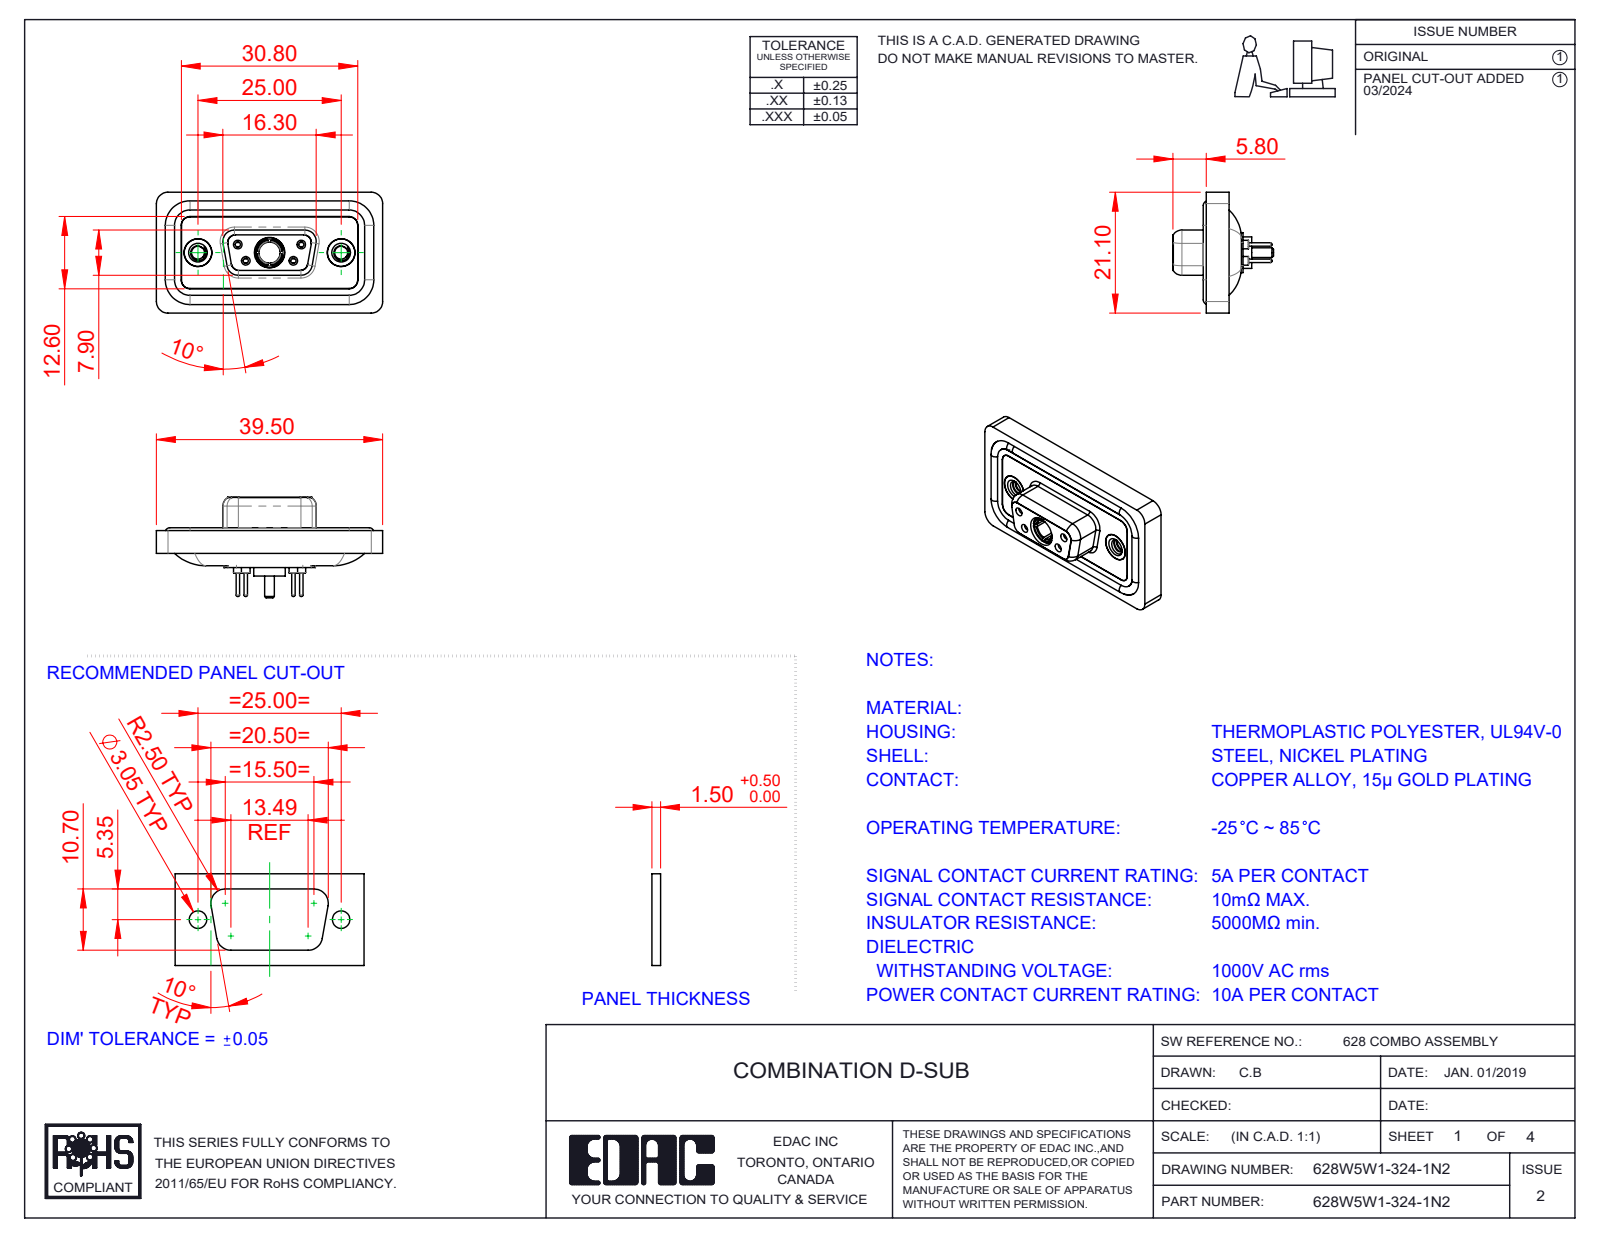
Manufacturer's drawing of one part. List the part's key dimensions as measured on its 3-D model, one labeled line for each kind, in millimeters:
Part name (STEP PRODUCT): 628Combo Shell Front_09 Contacts; 628Combo Threaded Rivet_2; 628Combo Contact Row 1_24; 628Combo Contact Row 2_24 (+5 more)
STEP written by: SolidWorks 2023 (CONFIG_CONTROL_DESIGN)
Units: millimetres
Bodies: 13 solids, 680 faces (194 planar, 287 cylindrical, 199 other)
Overall size (bounding box): 39.5 × 21.1 × 17.55
Volume: 4 752 mm³ · Surface area: 7 623 mm²
Round holes (diameter × count): ⌀0.9 ×4, ⌀1.1 ×4, ⌀1.5 ×4, ⌀2 ×4, ⌀4.85 ×3, ⌀1.6 ×2, ⌀1.7 ×2, ⌀2.26 ×2, ⌀4 ×2, ⌀4.05 ×2, ⌀5 ×2, ⌀3.7 ×1
Round bosses / shafts (diameter × count): ⌀1.6 ×6, ⌀2.2 ×4, ⌀0.6 ×4, ⌀4.95 ×2, ⌀4.8 ×2, ⌀5.5 ×1, ⌀5.2 ×1, ⌀4.96 ×1
Partial cylindrical surfaces — rounded edges, fillets, slot ends (radius × count): R1.5 ×22, R2 ×18, R1.35 ×8, R1.6 ×8, R0.25 ×4, R0.5 ×4, R0.6 ×4, R0.65 ×4
Main face-to-face distances: 0.4, 2.9, 1.8, 1.1, 1.6, 0.5, 5.65, 7.45, 5.35, 6.6
Hole centre spacings: 3.16, 5.72, 7.1, 12.5, 18.1, 4.39, 4.4, 8.31
